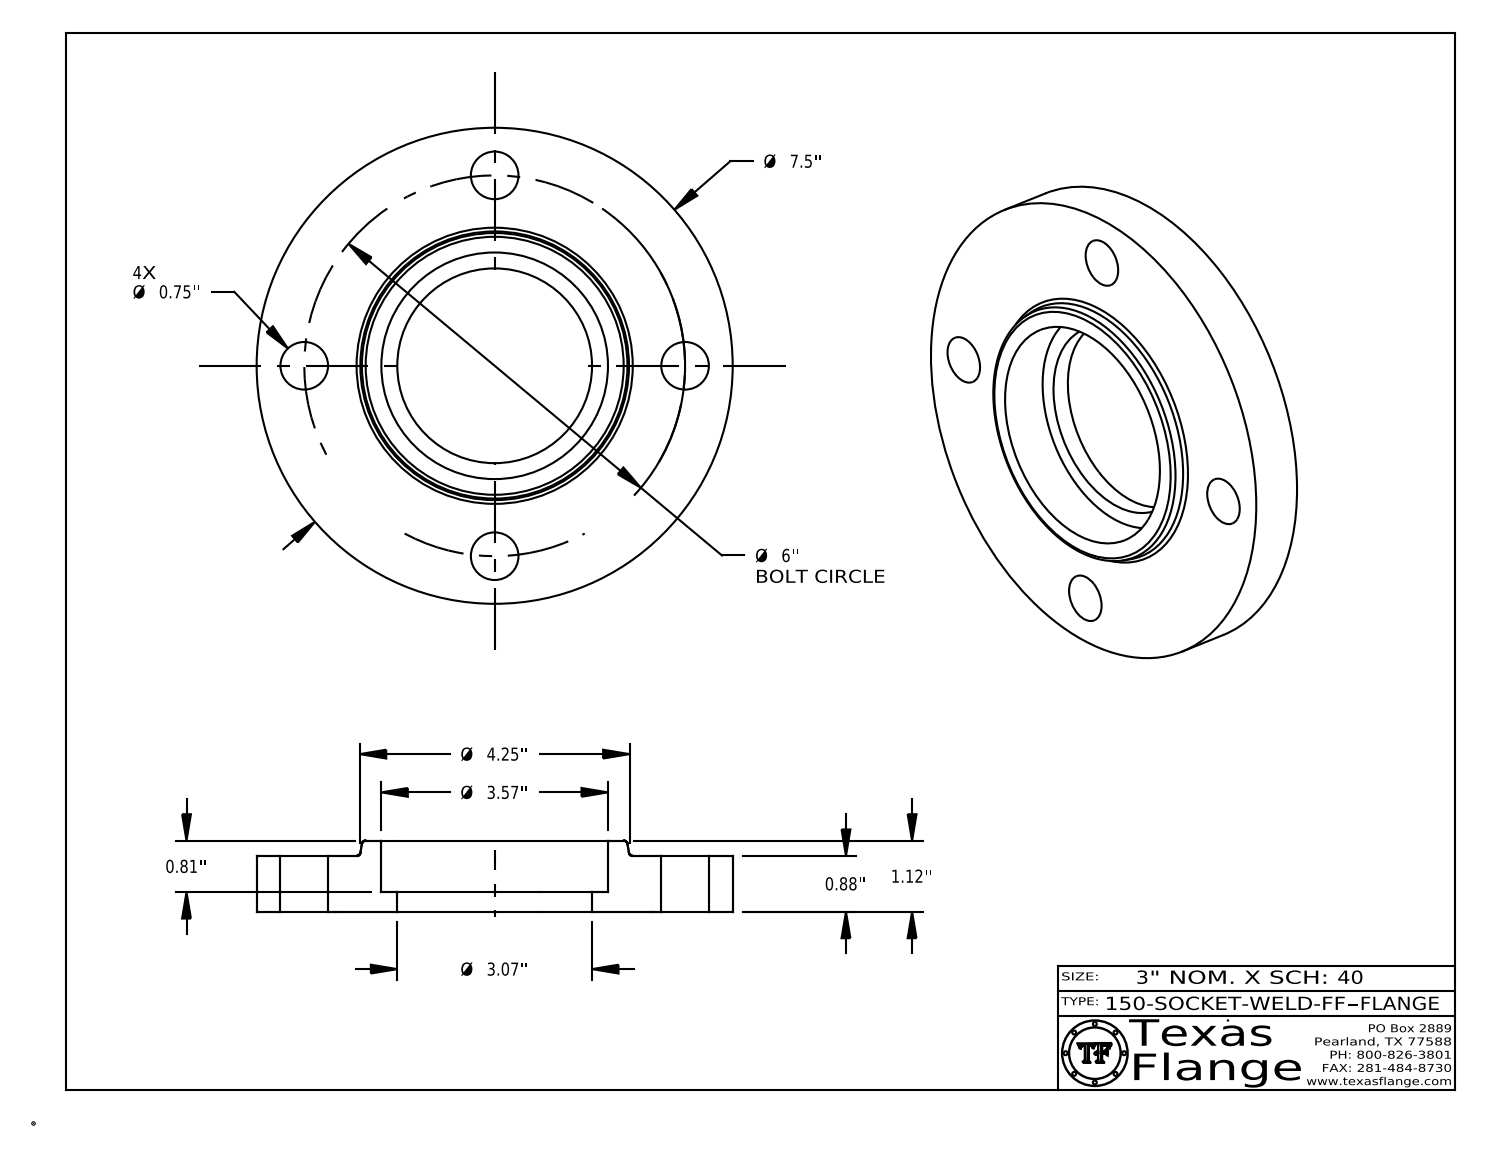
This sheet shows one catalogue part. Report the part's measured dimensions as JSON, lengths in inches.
{"part_name": "150-SOCKET-WELD-FF", "step_written_by": "CATIA V5 STEP AP214 (AUTOMOTIVE_DESIGN)", "units": "inches", "bodies": {"solids": 1, "faces": 410, "planar": 370, "cylindrical": 34, "other": 6}, "overall_size": [7.5, 7.5, 1.12], "volume_in3": 30.26, "surface_area_in2": 113.4, "round_holes": [[0.75, 4], [0.495, 1], [3.068, 1], [3.57, 1]], "round_bosses_or_shafts": [[0.03, 8], [7.5, 1], [0.39, 1]], "face_to_face_distances": [0.88, 1.12, 0.24, 0.31, 0.57, 0.81, 0.865, 0.555, 0.015, 0.255], "hole_center_spacings": [3, 4.243, 2.296, 5.543, 6]}
